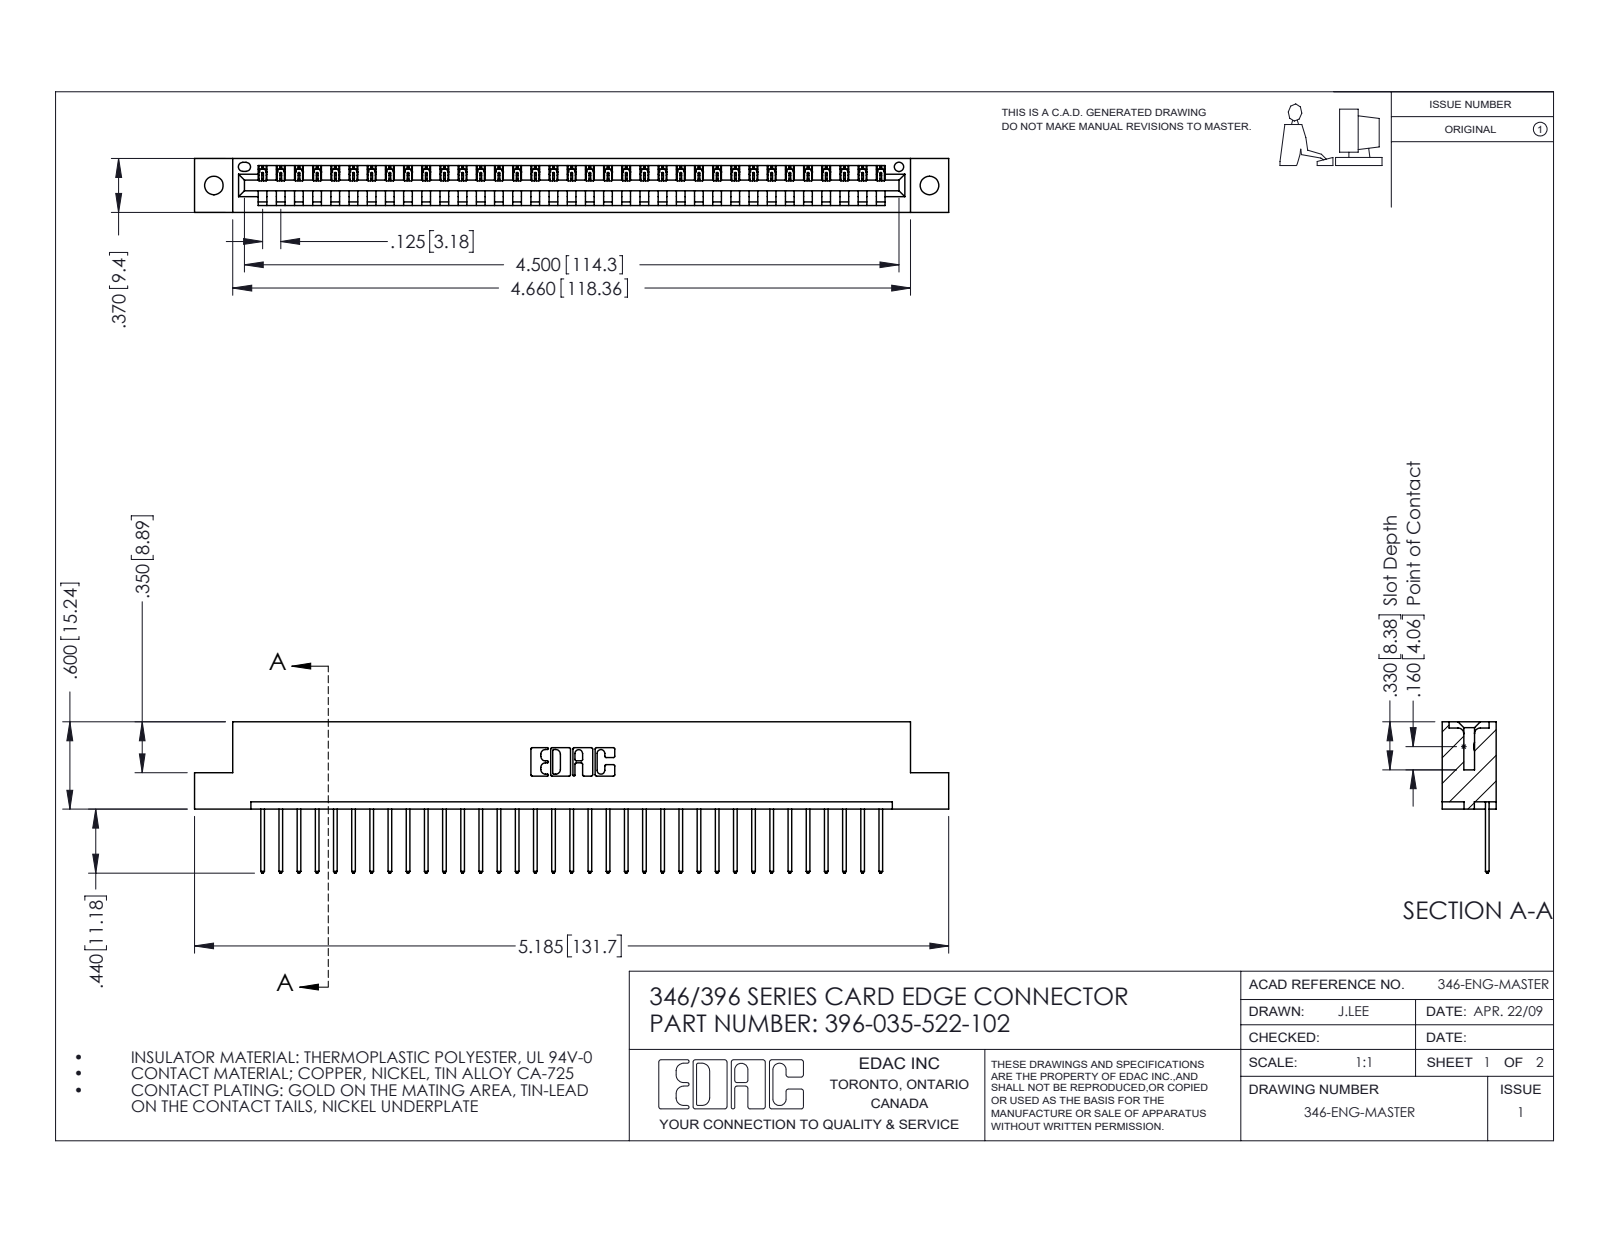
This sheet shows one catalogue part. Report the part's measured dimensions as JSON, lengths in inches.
{"part_name": "345-292-001_345-293-122; 396-035-522-102; 346 Part_Flush Mounting Lugs - 0.128 Dia", "step_written_by": "SolidWorks 2016 (CONFIG_CONTROL_DESIGN)", "units": "inches", "bodies": {"solids": 36, "faces": 2152, "planar": 1476, "cylindrical": 676, "other": 0}, "overall_size": [5.185, 1.04, 0.37], "volume_in3": 0.764, "surface_area_in2": 23.93, "round_holes": [[0.128, 2], [0.064, 1]], "partial_cylinders_radius": [[0.006, 70], [0.01, 70], [0.01, 22], [0.007, 6], [0.031, 6], [0.026, 3], [0.031, 2], [0.04, 2]], "face_to_face_distances": [0.048, 0.322, 0.37, 0.25, 0.072, 0.298, 0.025, 0.148, 0.222, 0.1], "hole_center_spacings": [0.246, 4.711, 4.92]}
